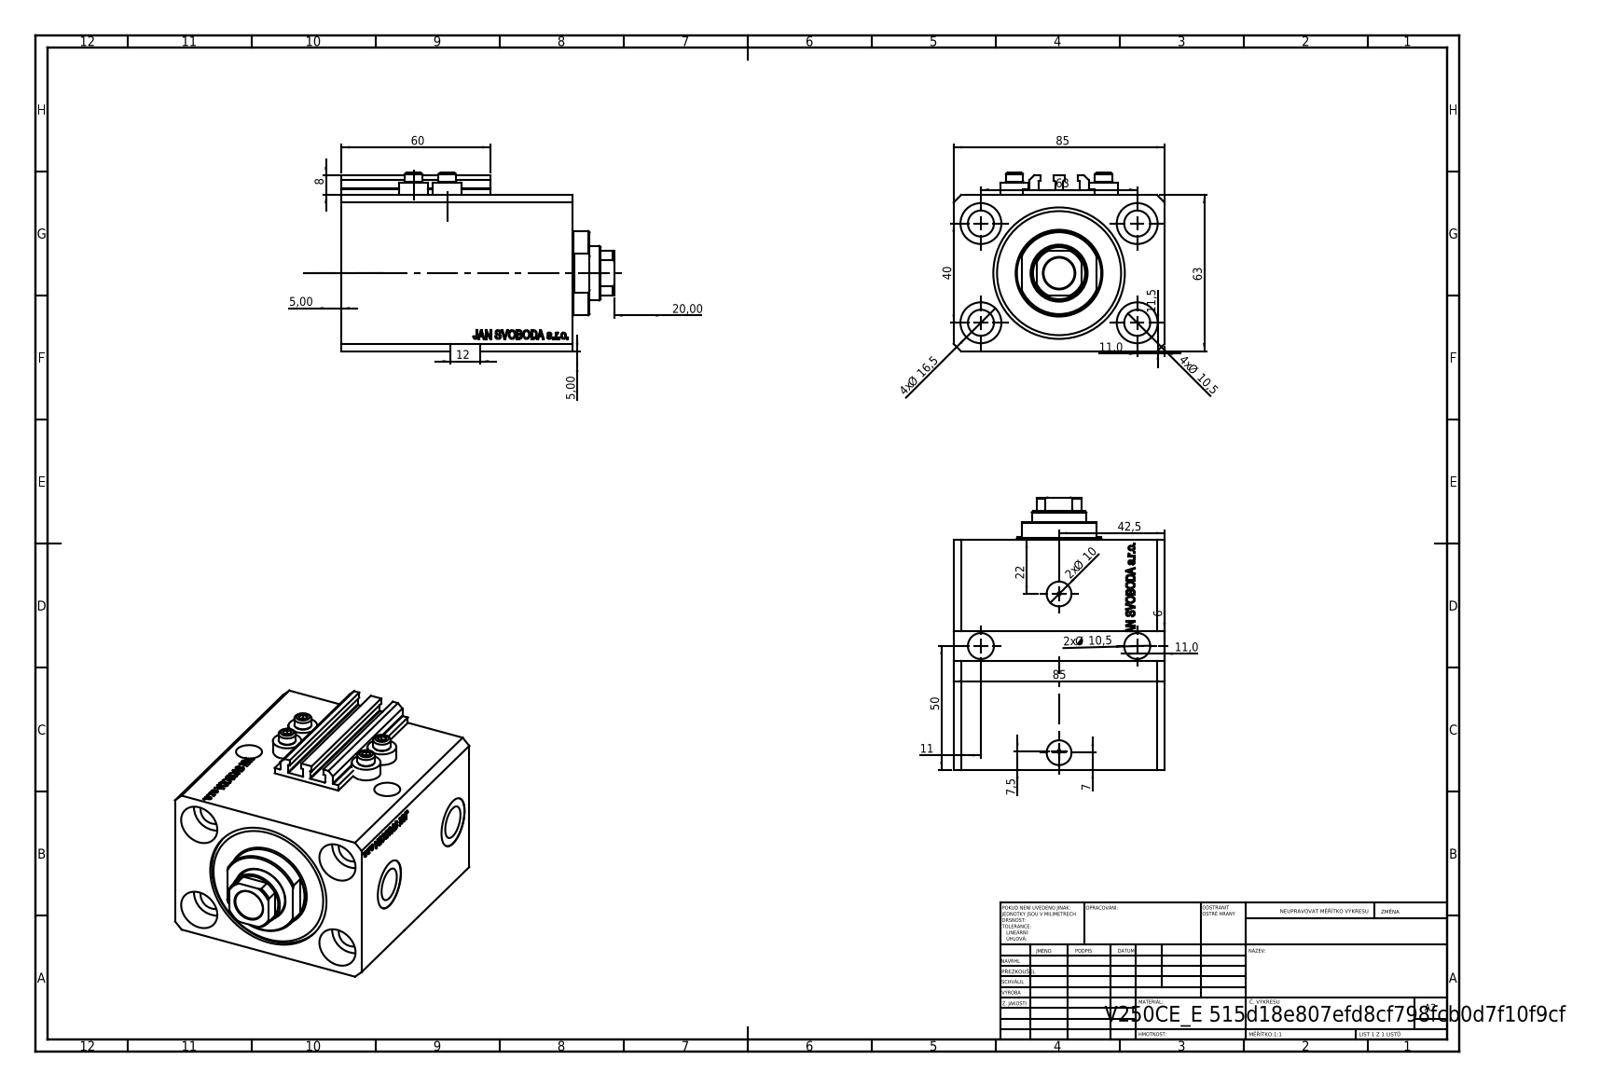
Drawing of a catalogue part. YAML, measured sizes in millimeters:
part_name: "V250CE_VC_E; ALLEN BOLT V250CE; V250CE_E; V250CE_C_VCP"
step_written_by: "SolidWorks 2019 (CONFIG_CONTROL_DESIGN)"
units: millimeters
bodies: {solids: 8, faces: 1087, planar: 535, cylindrical: 126, other: 426}
overall_size: [109.9, 85, 72]
volume: 437230
surface_area: 97950
round_holes:
  - {diameter: 10.5, count: 6}
  - {diameter: 1.25, count: 4}
  - {diameter: 4, count: 4}
  - {diameter: 16.5, count: 4}
  - {diameter: 10, count: 2}
  - {diameter: 13.16, count: 2}
  - {diameter: 20, count: 2}
  - {diameter: 12.5, count: 1}
  - {diameter: 22, count: 1}
  - {diameter: 40, count: 1}
  - {diameter: 53, count: 1}
round_bosses_or_shafts:
  - {diameter: 11.6, count: 4}
  - {diameter: 7, count: 4}
  - {diameter: 34, count: 1}
partial_cylinders:
  - {radius: 0.2, count: 10}
  - {radius: 10.5, count: 1}
face_to_face_distances: [63, 85, 93, 65.9, 54.5, 27.1, 11.4, 81.6, 3, 65]
hole_center_spacings: [37.31, 63, 13.6, 15.4, 24.96, 28.02, 28.43, 33.62]
